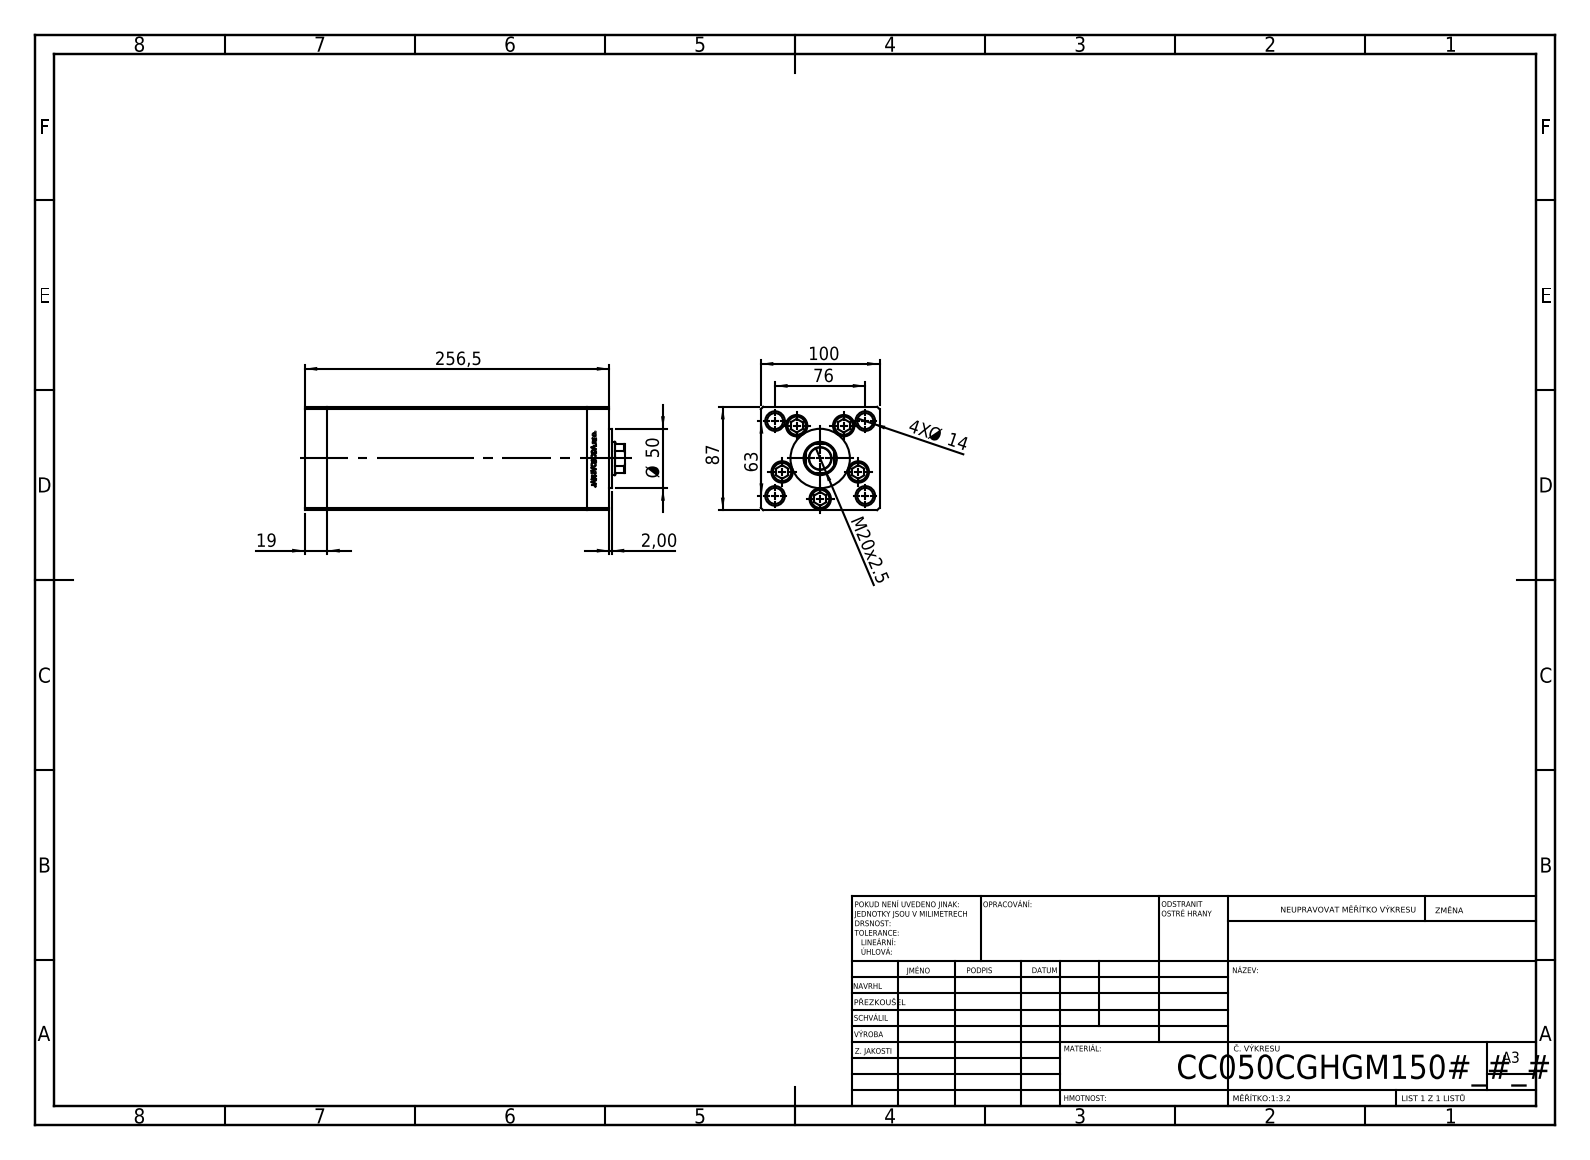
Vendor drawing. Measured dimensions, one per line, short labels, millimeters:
name: ALLEN BOLT; V220C BACK_C; V220C_C MIDDLE; V220C_VC_C (+1 more)
written by: SolidWorks 2019 (CONFIG_CONTROL_DESIGN)
unit: mm
bodies: 13 solids, 1186 faces (548 planar, 176 cylindrical, 462 other)
size: 269.5 × 100 × 87
volume: 1 820 000 mm³; area: 279 473 mm²
holes: 9× ⌀13.5, 5× ⌀18, 4× ⌀2, 4× ⌀12, 4× ⌀13.16, 4× ⌀16.5, 1× ⌀17, 1× ⌀18.5, 1× ⌀28
bosses: 5× ⌀8, 4× ⌀17, 1× ⌀50
rounds: 2× R0.93, 1× R13.5
face distances: 100, 87, 19, 218.5, 237.5, 34.25, 256.5, 222.25, 203.25, 15.25
hole spacings: 34, 49.36, 18.59, 21.03, 38.08, 39.27, 40.83, 43.24
